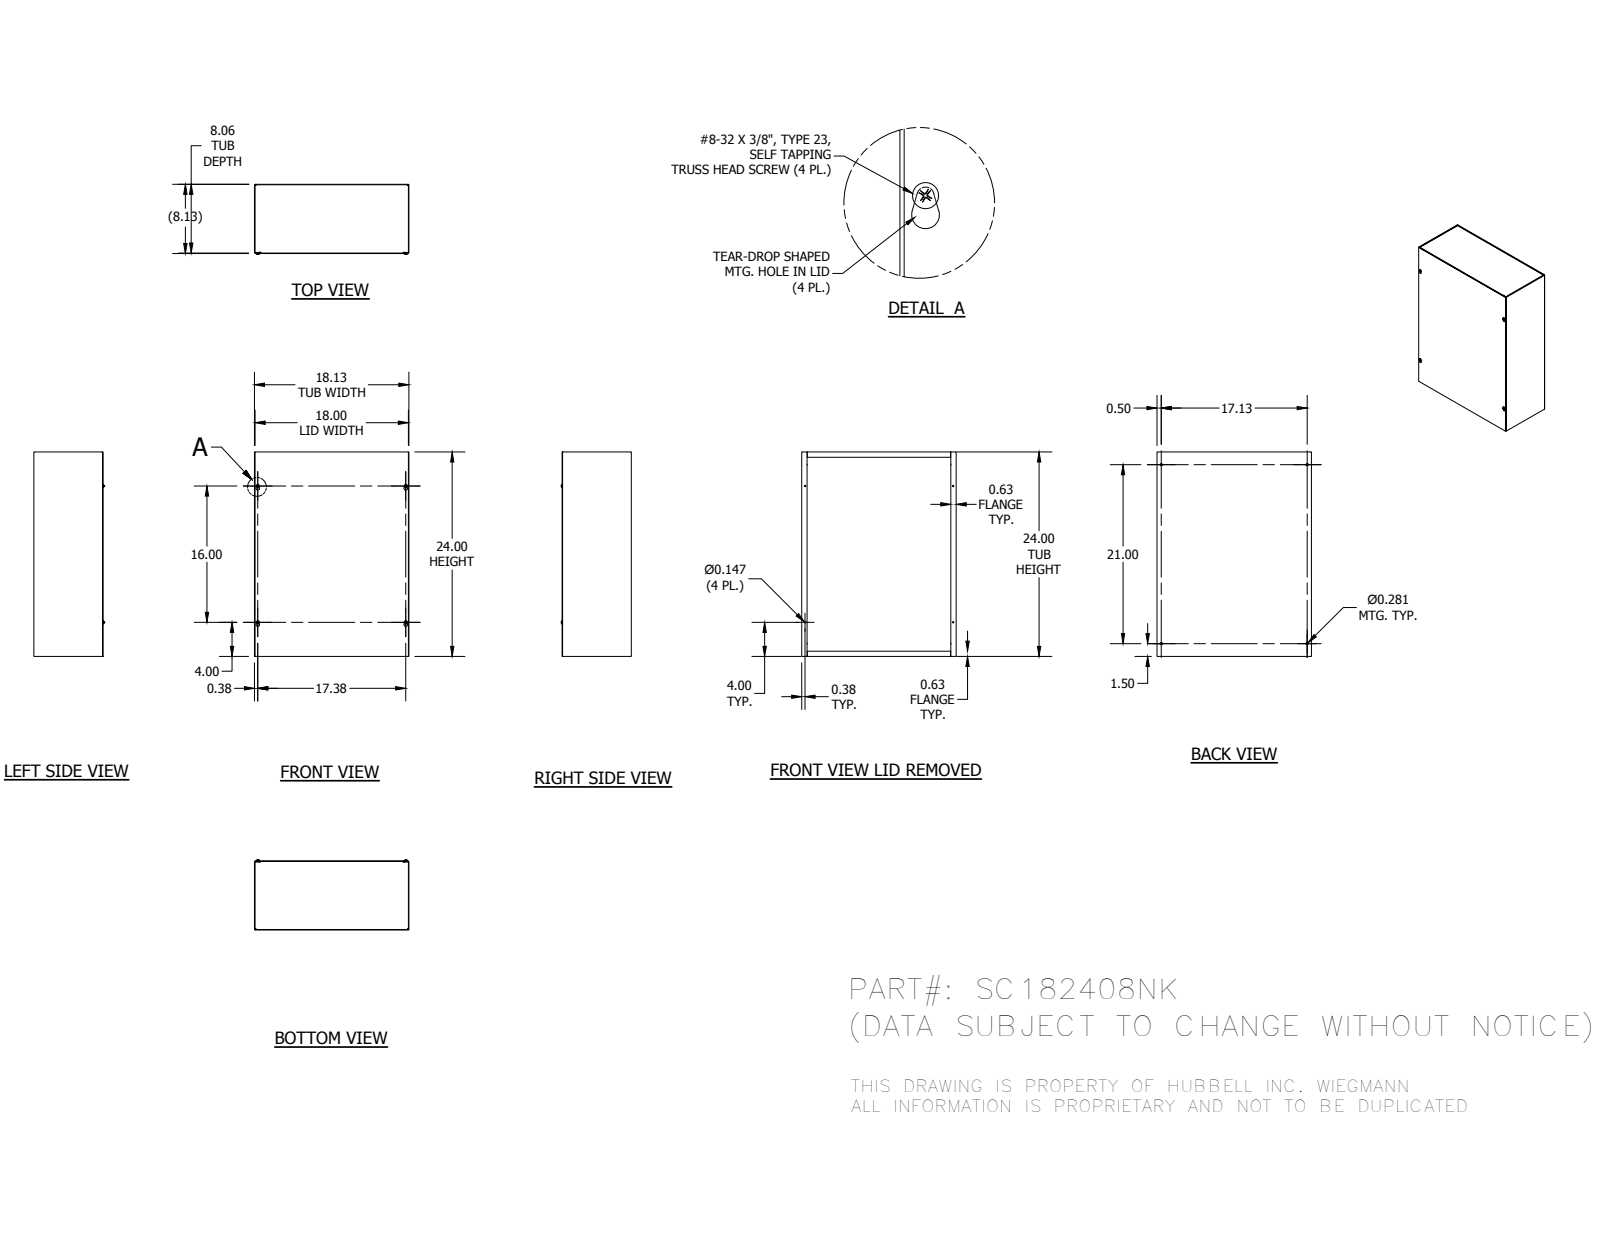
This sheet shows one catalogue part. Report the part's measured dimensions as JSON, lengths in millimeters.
{"part_name": "SC182408NKBLR; SC1808NKTB; SC1824LPA; 34056 (+1 more)", "step_written_by": "Autodesk Inventor 2014 (AUTOMOTIVE_DESIGN)", "units": "millimeters", "bodies": {"solids": 8, "faces": 268, "planar": 152, "cylindrical": 48, "other": 68}, "overall_size": [609.6, 460.38, 208.92], "volume_mm3": 1656000, "surface_area_mm2": 2100000, "round_holes": [[3.73, 4], [7.14, 4]], "round_bosses_or_shafts": [[9.75, 4], [4.17, 4]], "partial_cylinders_radius": [[0.79, 12], [2.38, 12], [3.17, 4], [5.16, 4]], "face_to_face_distances": [1.59, 204.79, 203.2, 206.38, 458.79, 608.01, 457.2, 460.38, 609.6, 606.42], "hole_center_spacings": [63.58, 442.73, 469.91, 642.48, 406.4, 434.98, 441.32, 533.4]}
